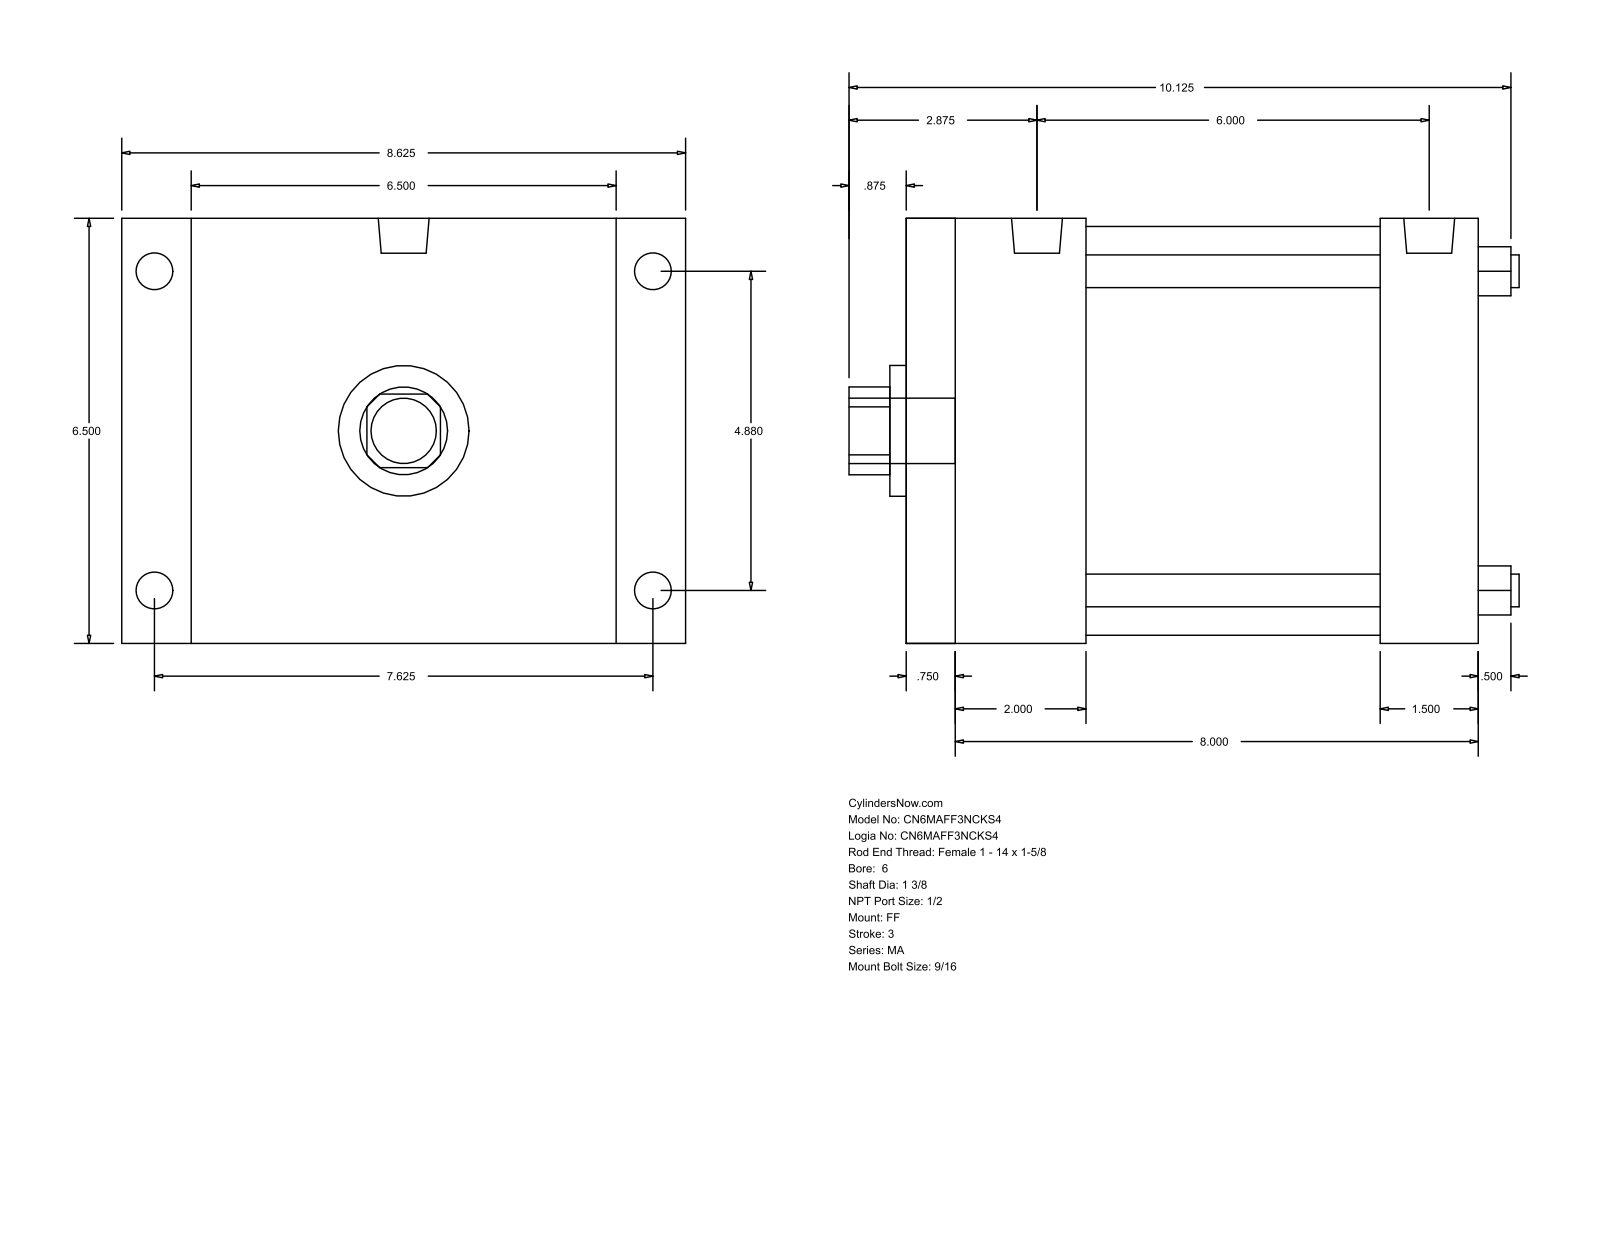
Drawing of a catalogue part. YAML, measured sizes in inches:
part_name: "MA_FF__0600_1.375"
step_written_by: "GSSL Pune (CONFIG_CONTROL_DESIGN)"
units: inches
bodies: {solids: 0, faces: 92, planar: 64, cylindrical: 28, other: 0}
overall_size: [10.25, 8.625, 6.5]
round_holes:
  - {diameter: 0.5, count: 4}
  - {diameter: 1.375, count: 1}
  - {diameter: 2, count: 1}
  - {diameter: 6.25, count: 1}
round_bosses_or_shafts:
  - {diameter: 0.687, count: 4}
  - {diameter: 0.563, count: 4}
  - {diameter: 0.778, count: 2}
  - {diameter: 1, count: 1}
partial_cylinders:
  - {radius: 0.672, count: 1}
face_to_face_distances: [6.5, 8.75, 0.625, 8.125, 2, 6.625, 2.625, 6.125, 7.25, 4.625]
hole_center_spacings: [3.451, 4.88, 6.902]
